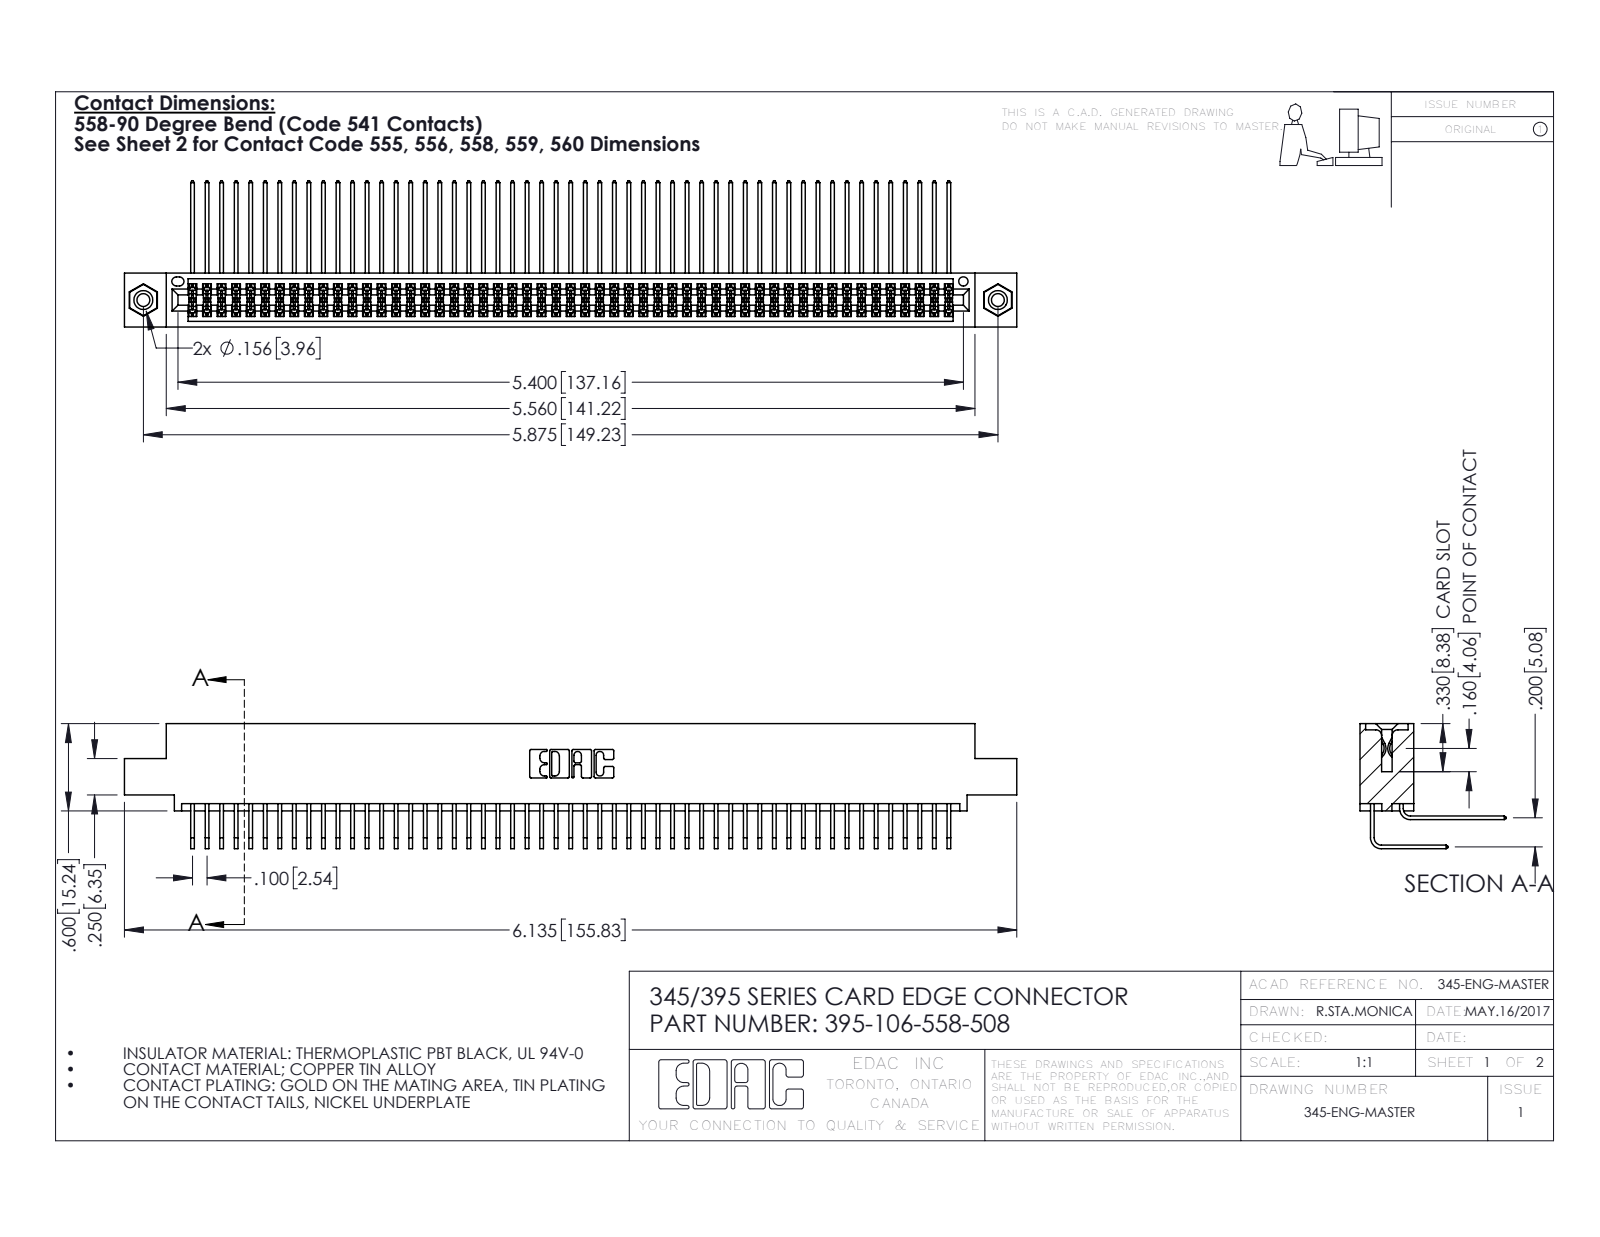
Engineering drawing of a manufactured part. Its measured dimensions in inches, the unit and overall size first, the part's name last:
Units: inches
Overall size (bounding box): 6.135 × 1.005 × 0.859
Round holes (diameter × count): ⌀0.089 ×2, ⌀0.125 ×2, ⌀0.156 ×2, ⌀0.064 ×1
Round bosses / shafts (diameter × count): ⌀0.155 ×2
Partial cylindrical surfaces — rounded edges, fillets, slot ends (radius × count): R0.006 ×160, R0.01 ×22, R0.007 ×6, R0.031 ×6, R0.026 ×3, R0.014 ×2, R0.019 ×2, R0.022 ×2
Main face-to-face distances: 0.072, 0.298, 0.2, 0.37, 0.098, 0.272, 0.025, 0.225, 0.025, 0.175
Hole centre spacings: 0.27, 5.639, 5.875
Volume: 0.962 in³ · Surface area: 41.09 in²
Bodies: 109 solids, 5702 faces (3826 planar, 1860 cylindrical, 16 other)
Part name (STEP PRODUCT): 345-292-001_558 Tail - 2; 345 Part_0.110 Offset - 0.156 Dia-TI; 345-250-001_345-250-003-102; 395-106-558-508 (+1 more)
STEP written by: SolidWorks 2016 (CONFIG_CONTROL_DESIGN)
